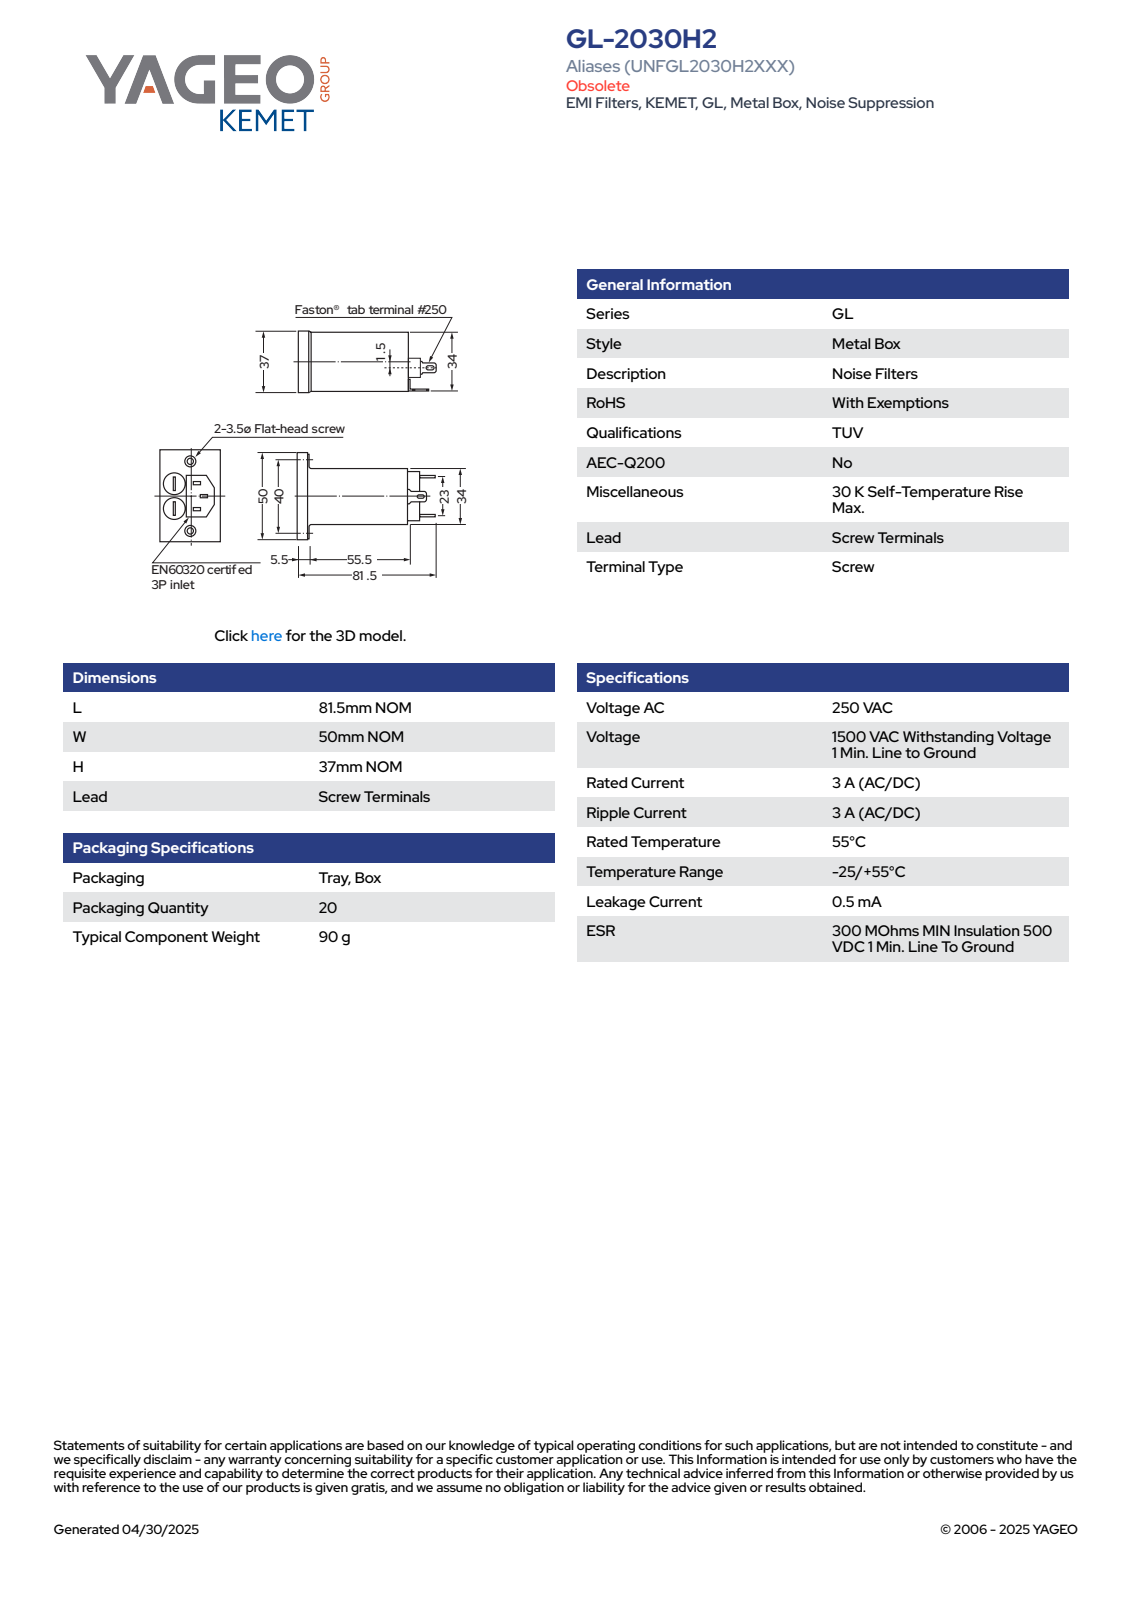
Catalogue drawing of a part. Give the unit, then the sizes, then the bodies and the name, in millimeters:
Units: millimetres
Overall size (bounding box): 81.5 × 50 × 37
Round holes (diameter × count): ⌀3.5 ×2
Partial cylindrical surfaces — rounded edges, fillets, slot ends (radius × count): R1 ×30, R0.5 ×4, R3 ×4, R1.5 ×2
Main face-to-face distances: 34, 61, 5.5, 55.5, 4.5, 12, 10, 51, 1.5, 35.5
Hole centre spacings: 37.46
Volume: 72 396 mm³ · Surface area: 14 324 mm²
Bodies: 1 solid, 180 faces (118 planar, 50 cylindrical, 12 other)
Part name (STEP PRODUCT): ENF_KGLH_L81.5W50H37
STEP written by: SolidWorks 2014 (AUTOMOTIVE_DESIGN)
